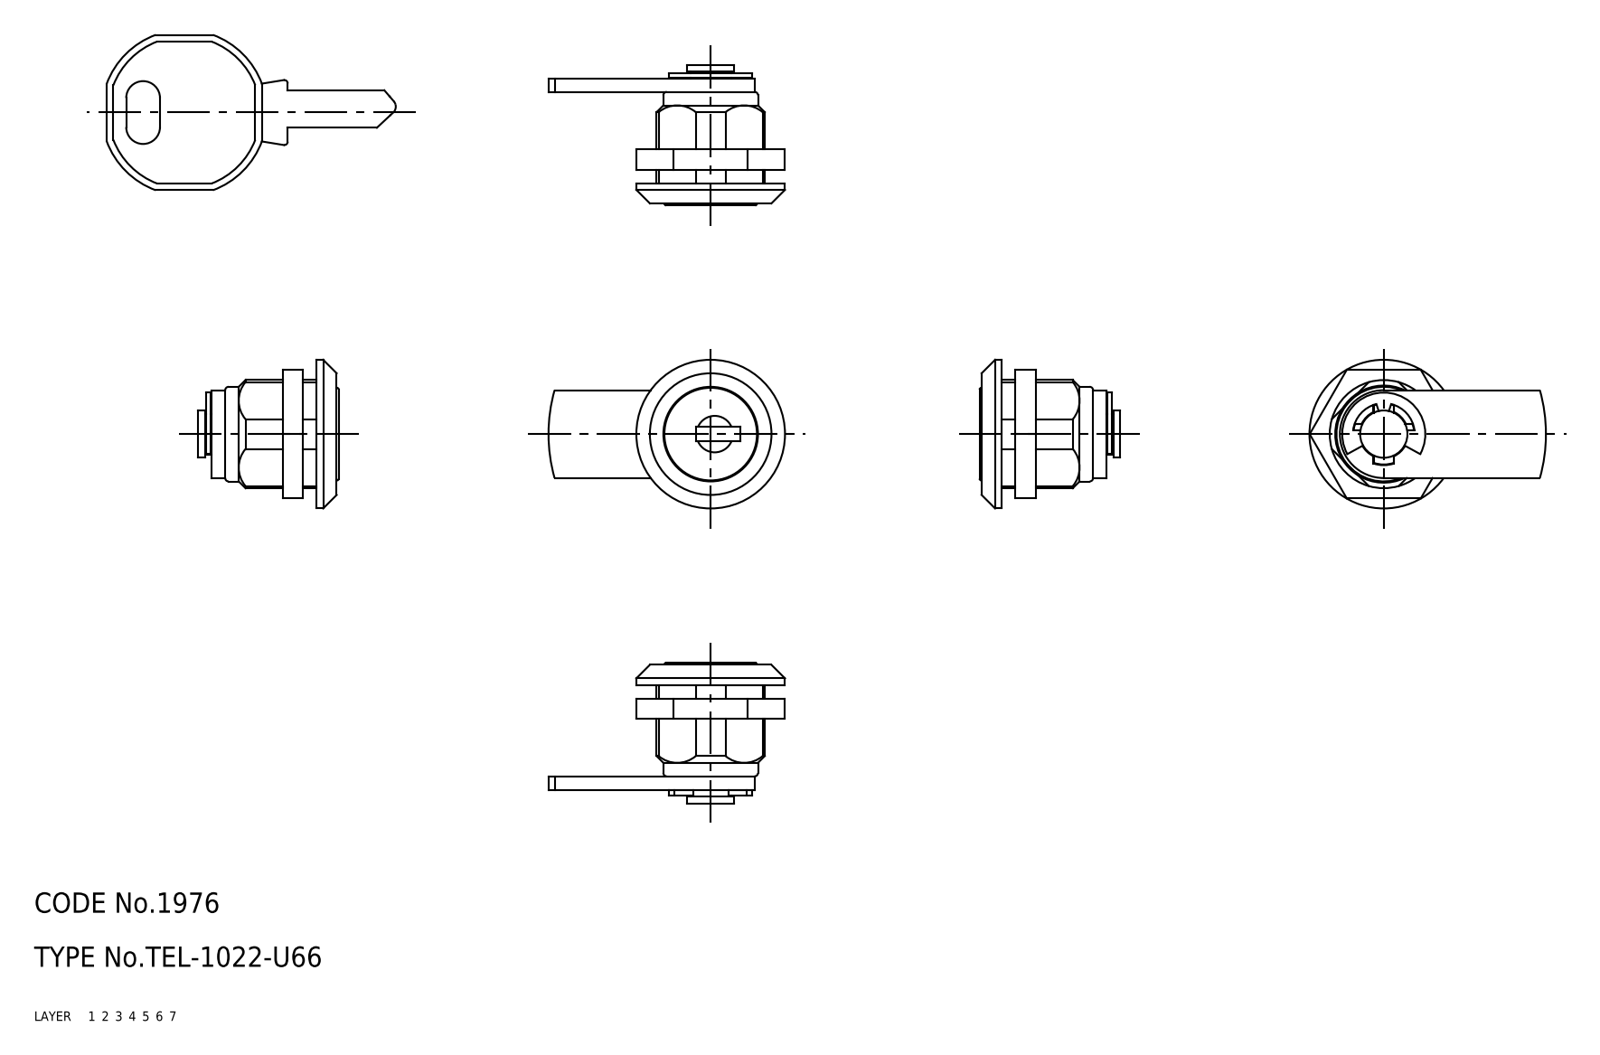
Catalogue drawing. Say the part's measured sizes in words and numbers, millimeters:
The part is named "nut; lock; key; housing (+2 more)". Its 3-D file was written by "CADfix (AUTOMOTIVE_DESIGN)". It is 5 solids with 154 faces: 0 planar, 0 cylindrical and 154 other. Overall it measures 74.57 by 36.62 by 22 millimeters. Its volume is 6 648 cubic millimeters and its surface area 6 187 square millimeters.
